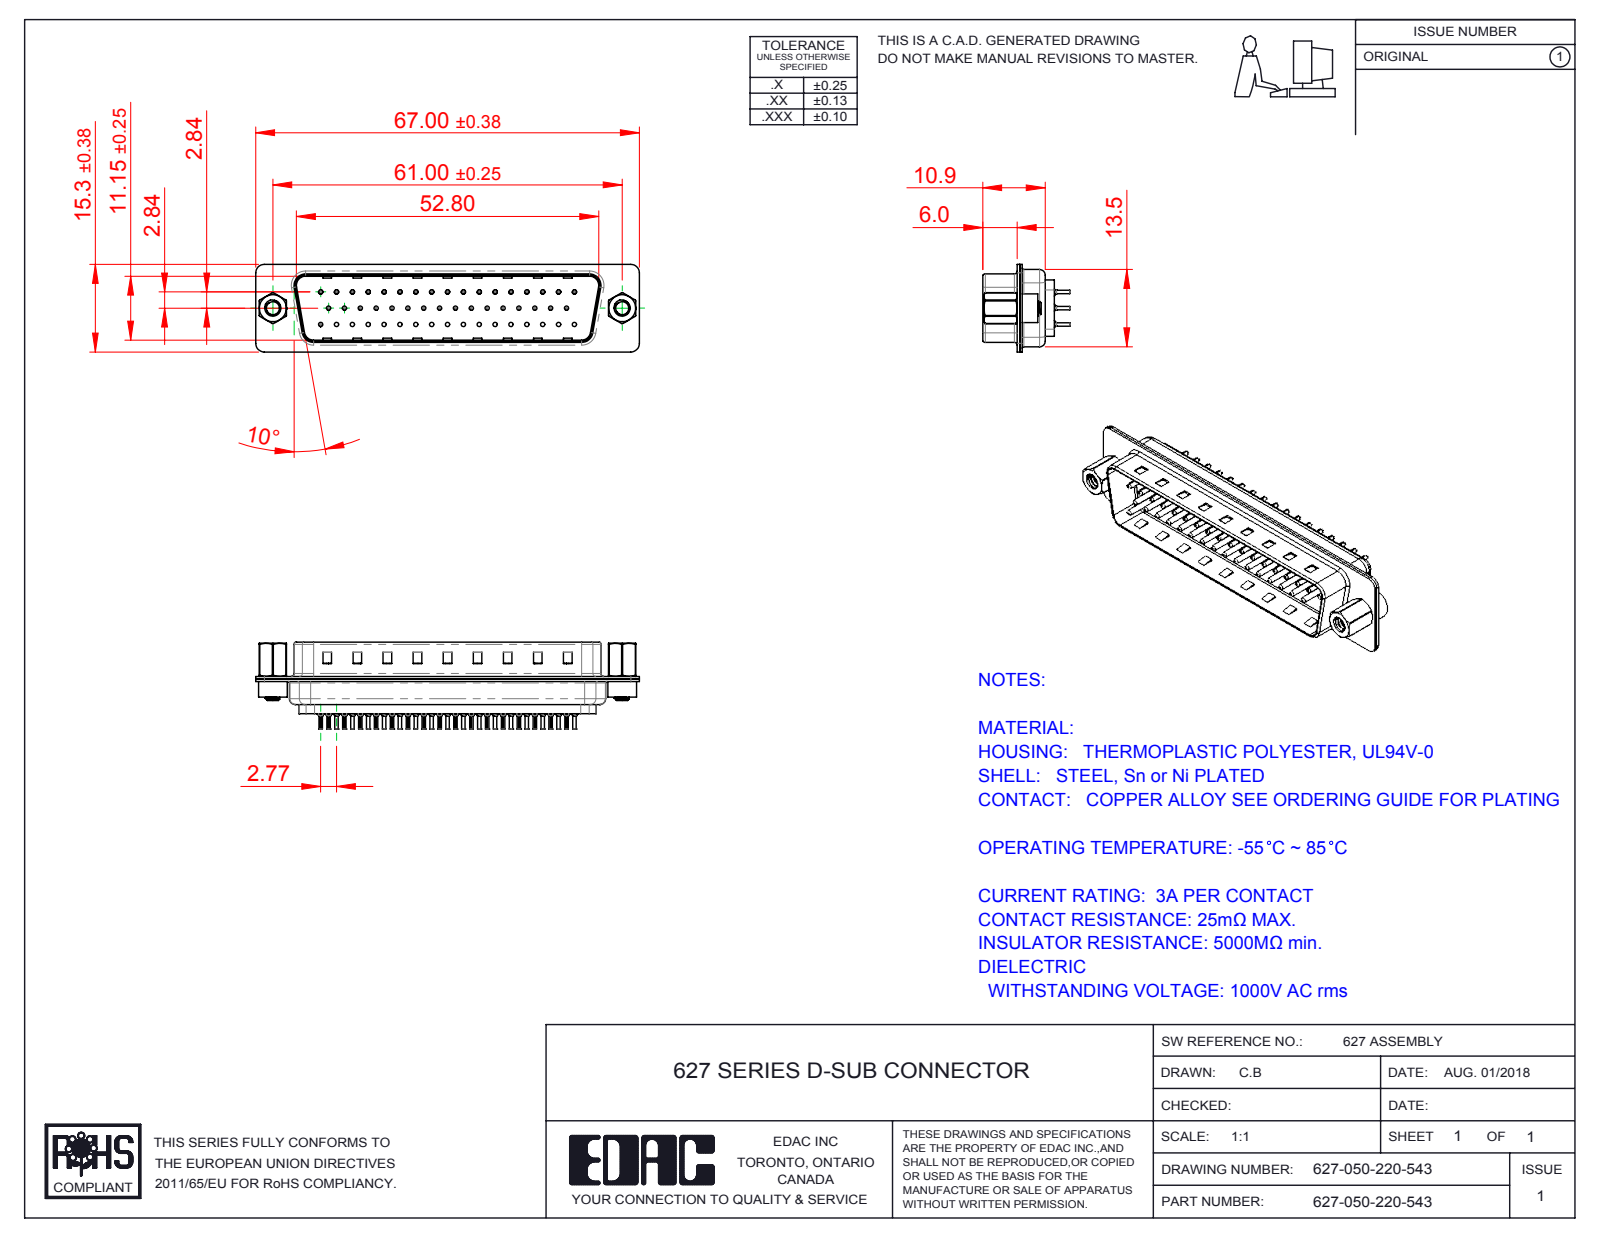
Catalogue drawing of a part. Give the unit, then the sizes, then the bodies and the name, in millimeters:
Units: millimetres
Overall size (bounding box): 67 × 15.3 × 15.2
Round holes (diameter × count): ⌀1.6 ×50, ⌀0.2 ×34, ⌀0.35 ×34, ⌀1.1 ×34, ⌀0.75 ×16, ⌀2 ×16, ⌀2.26 ×2, ⌀2.29 ×2, ⌀4 ×2, ⌀4.8 ×2
Round bosses / shafts (diameter × count): ⌀2 ×34, ⌀1.5 ×34, ⌀0.75 ×34, ⌀0.6 ×34, ⌀5 ×2, ⌀4.9 ×2, ⌀2.79 ×2
Partial cylindrical surfaces — rounded edges, fillets, slot ends (radius × count): R0.1 ×68, R1.5 ×16, R2 ×12, R0.5 ×8, R1.6 ×8, R0.25 ×4, R0.6 ×4, R0.65 ×4
Main face-to-face distances: 0.4, 0.45, 11.55, 0.9, 6.05, 6.5, 12.33, 0.78, 0.77, 12.32
Hole centre spacings: 3.16, 2.77, 5.54, 8.31, 11.08, 13.85, 16.62, 5.03
Volume: 4 491 mm³ · Surface area: 11 445 mm²
Bodies: 41 solids, 3998 faces (1073 planar, 1567 cylindrical, 1358 other)
Part name (STEP PRODUCT): 627 Housing_50 LP; 627-050-220-543; 627 4-40 Hex Standoff; 627 Shell Front_50 Contacts (+5 more)
STEP written by: SolidWorks 2016 (CONFIG_CONTROL_DESIGN)
